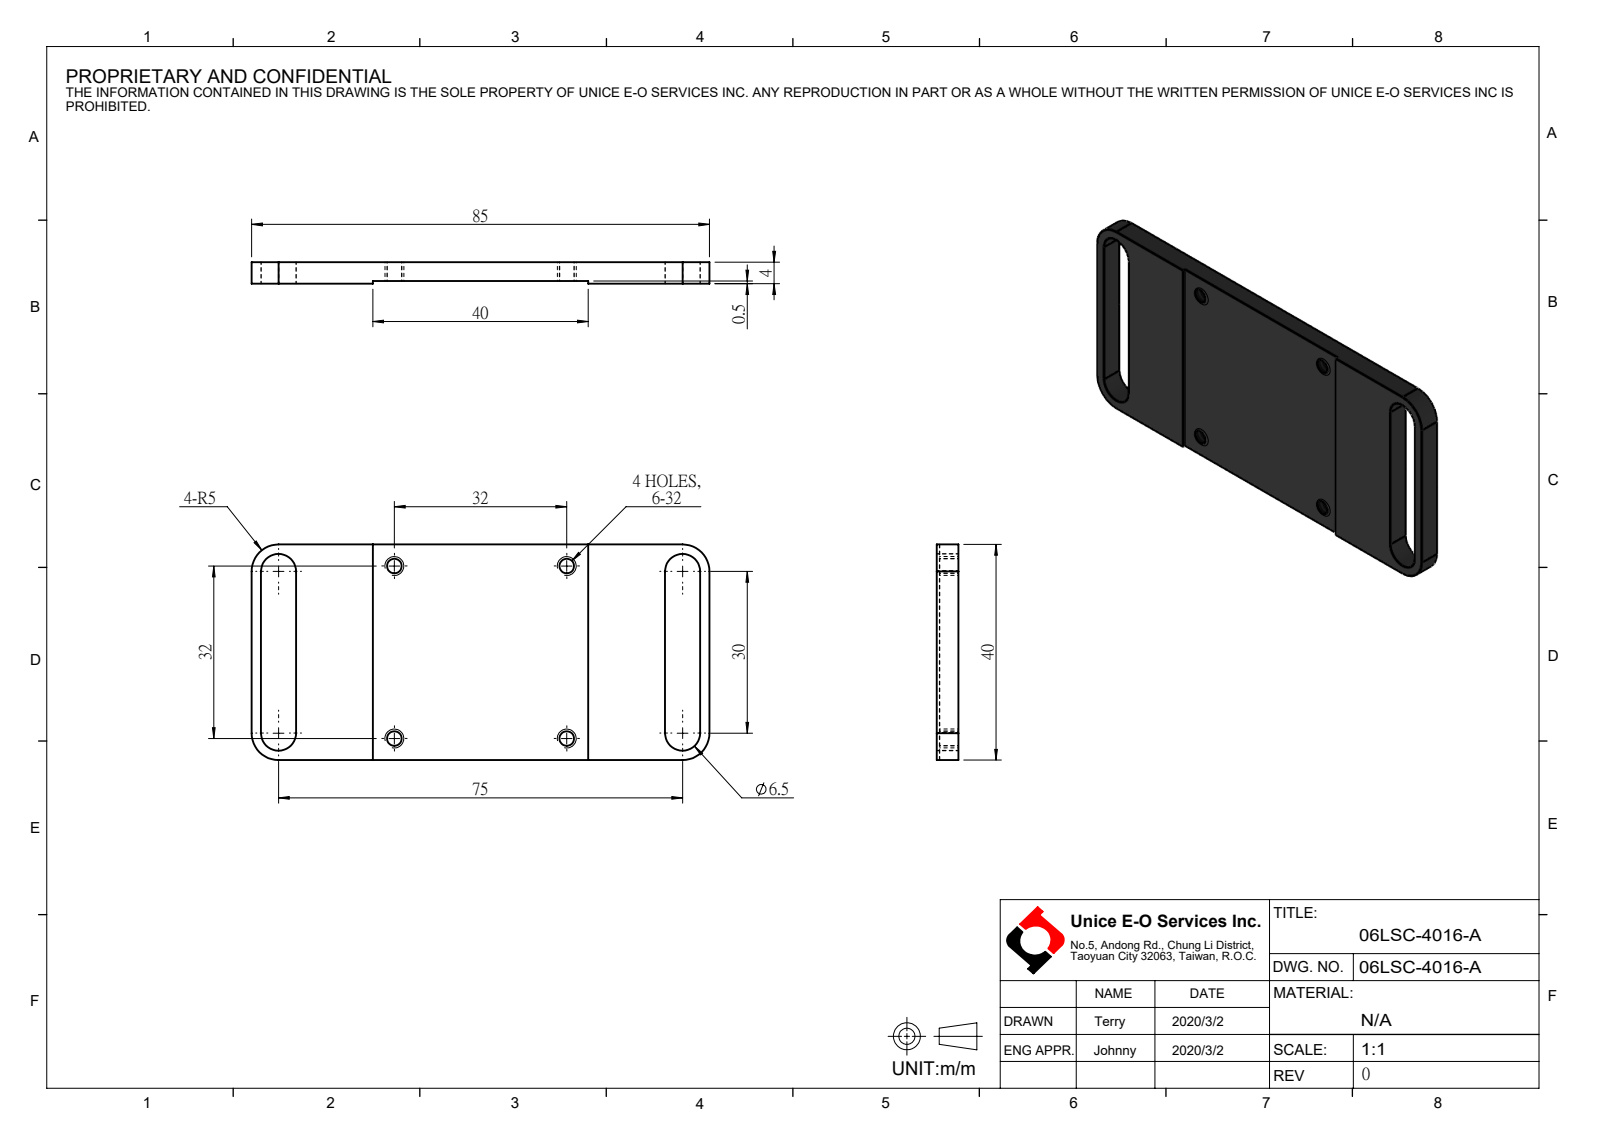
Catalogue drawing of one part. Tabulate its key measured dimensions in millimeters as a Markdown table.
| quantity | value |
| --- | --- |
| part name | 06LSC-4016-A |
| STEP written by | SolidWorks 2016 (CONFIG_CONTROL_DESIGN) |
| units | millimeters |
| bodies | 1 solid, 32 faces (14 planar, 18 cylindrical, 0 other) |
| overall size | 85 × 40 × 4 |
| volume | 10 833 mm³ |
| surface area | 7 521 mm² |
| round holes (diameter × count) | 2.26 × 4 |
| partial cylindrical surfaces (radius × count) | 3.25 × 4, 5 × 4 |
| main face-to-face distances | 3.5, 4, 0.5, 40, 1.75, 8.25, 76.75, 83.25, 6.5, 75 |
| hole center spacings | 32, 45.25 |
